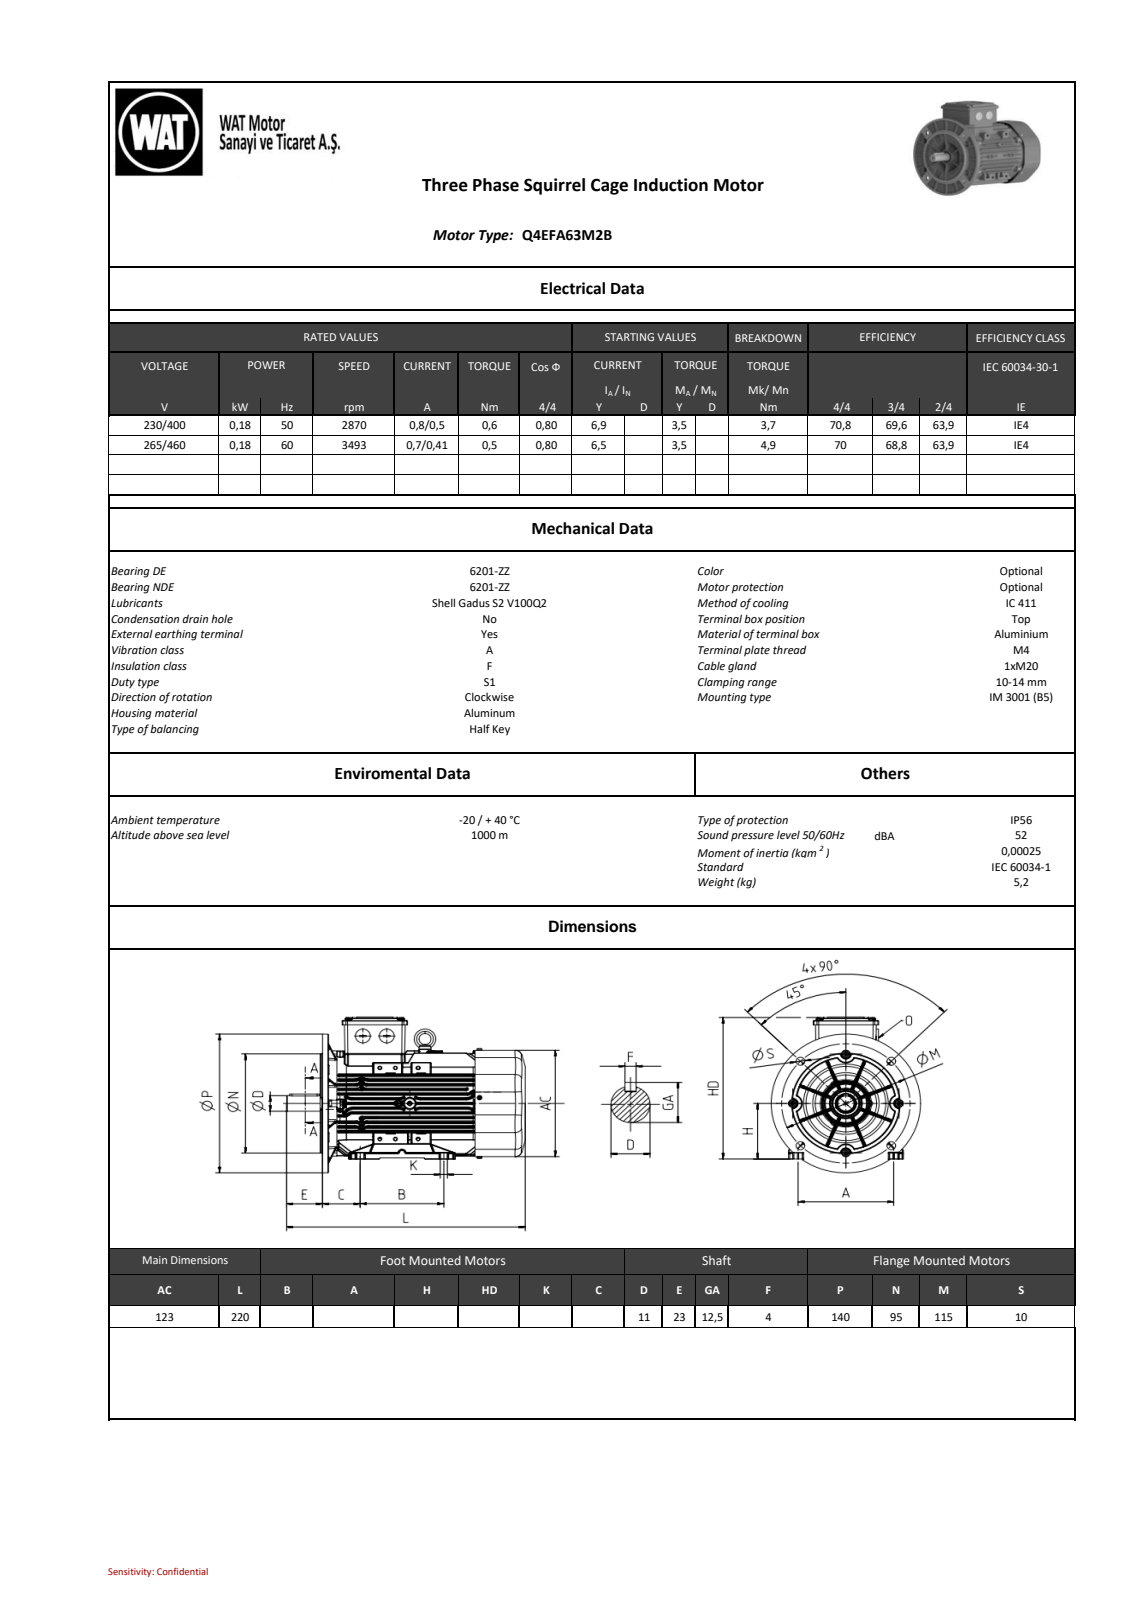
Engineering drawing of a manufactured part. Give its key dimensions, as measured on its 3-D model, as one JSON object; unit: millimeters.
{"part_name": "QE series_ 63_B5_stp_objects", "step_written_by": "SIEMENS PLM Software NX2206.8101 (AP203_CONFIGURATION_CONTROLLED_3D_DESIGN_OF_MECHANICAL_PARTS_AND_ASSEMBLIES_MIM_LF)", "units": "millimeters", "bodies": {"solids": 0, "faces": 1289, "planar": 742, "cylindrical": 335, "other": 212}, "overall_size": [219.46, 167.2, 140.2], "round_holes": [[3.65, 8], [10, 8], [2.5, 4], [3, 2], [8, 1], [11.2, 1], [14.5, 1]], "round_bosses_or_shafts": [[8, 8], [4, 4], [140.2, 1], [123, 1], [121, 1], [95, 1], [26, 1], [19, 1]], "partial_cylinders_radius": [[0.5, 45], [1, 39], [1.5, 28], [2, 14], [1.35, 12], [0.1, 8], [2.5, 8], [4, 8]], "face_to_face_distances": [27.96, 13.97, 14.16, 6.93, 6.88, 21.03, 7.01, 20.9, 7.06, 35.06], "hole_center_spacings": [44.01, 57.5, 81.32, 106.25, 54, 63, 82.98, 115]}
